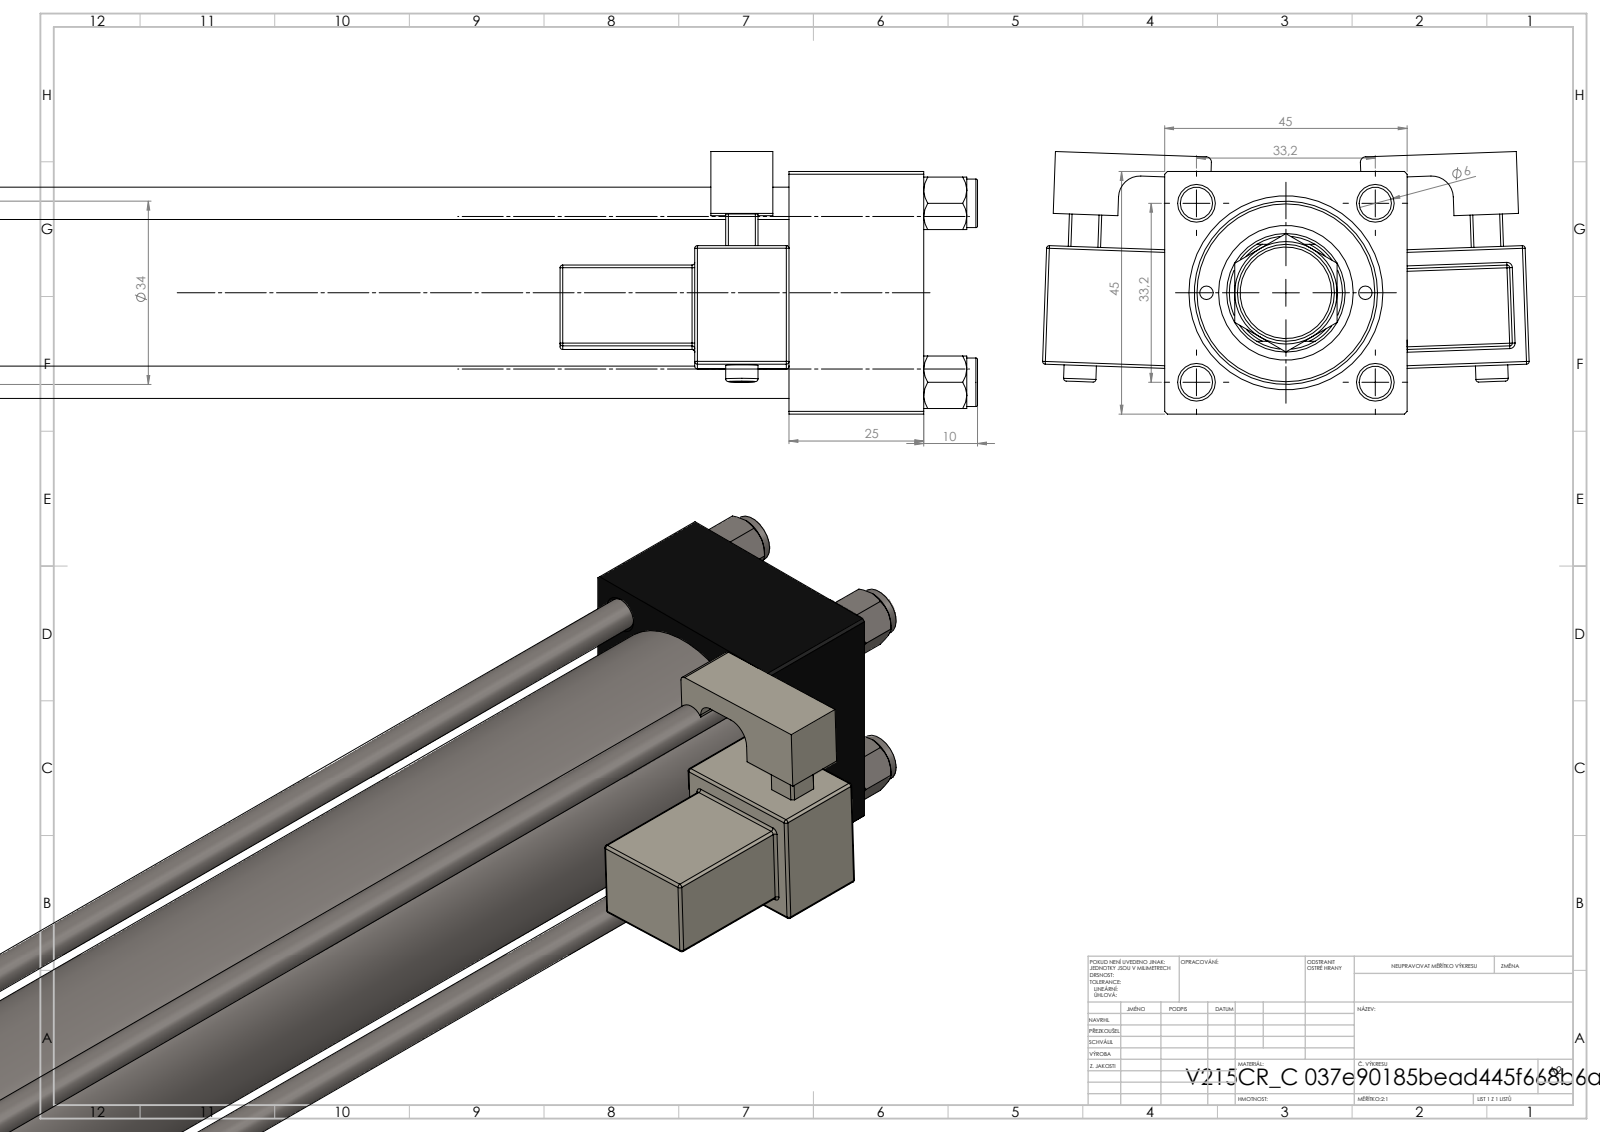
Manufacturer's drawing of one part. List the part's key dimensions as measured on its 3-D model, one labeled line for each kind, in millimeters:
Part name (STEP PRODUCT): V215_VC_A; V215CR_MSU; MFA; NUT_M5_C (+3 more)
STEP written by: SolidWorks 2019 (CONFIG_CONTROL_DESIGN)
Units: millimetres
Bodies: 14 solids, 1363 faces (605 planar, 154 cylindrical, 604 other)
Overall size (bounding box): 471 × 90.31 × 48.72
Volume: 488 886 mm³ · Surface area: 188 306 mm²
Round holes (diameter × count): ⌀6 ×4, ⌀2.5 ×2, ⌀7 ×2, ⌀13.16 ×2, ⌀20 ×2, ⌀10.5 ×1, ⌀22 ×1, ⌀24 ×1, ⌀25 ×1, ⌀32 ×1, ⌀33 ×1
Round bosses / shafts (diameter × count): ⌀9 ×4, ⌀6 ×2, ⌀38 ×1, ⌀34 ×1, ⌀18 ×1, ⌀11 ×1
Partial cylindrical surfaces — rounded edges, fillets, slot ends (radius × count): R0.5 ×48, R1 ×2, R2.5 ×2, R4 ×2, R10.5 ×1
Main face-to-face distances: 45, 25, 3, 355, 330, 403, 22.99, 312.5, 378, 13
Hole centre spacings: 16.7, 23.48, 33.2, 35.47, 14.75, 46.95, 29.5, 355.5
